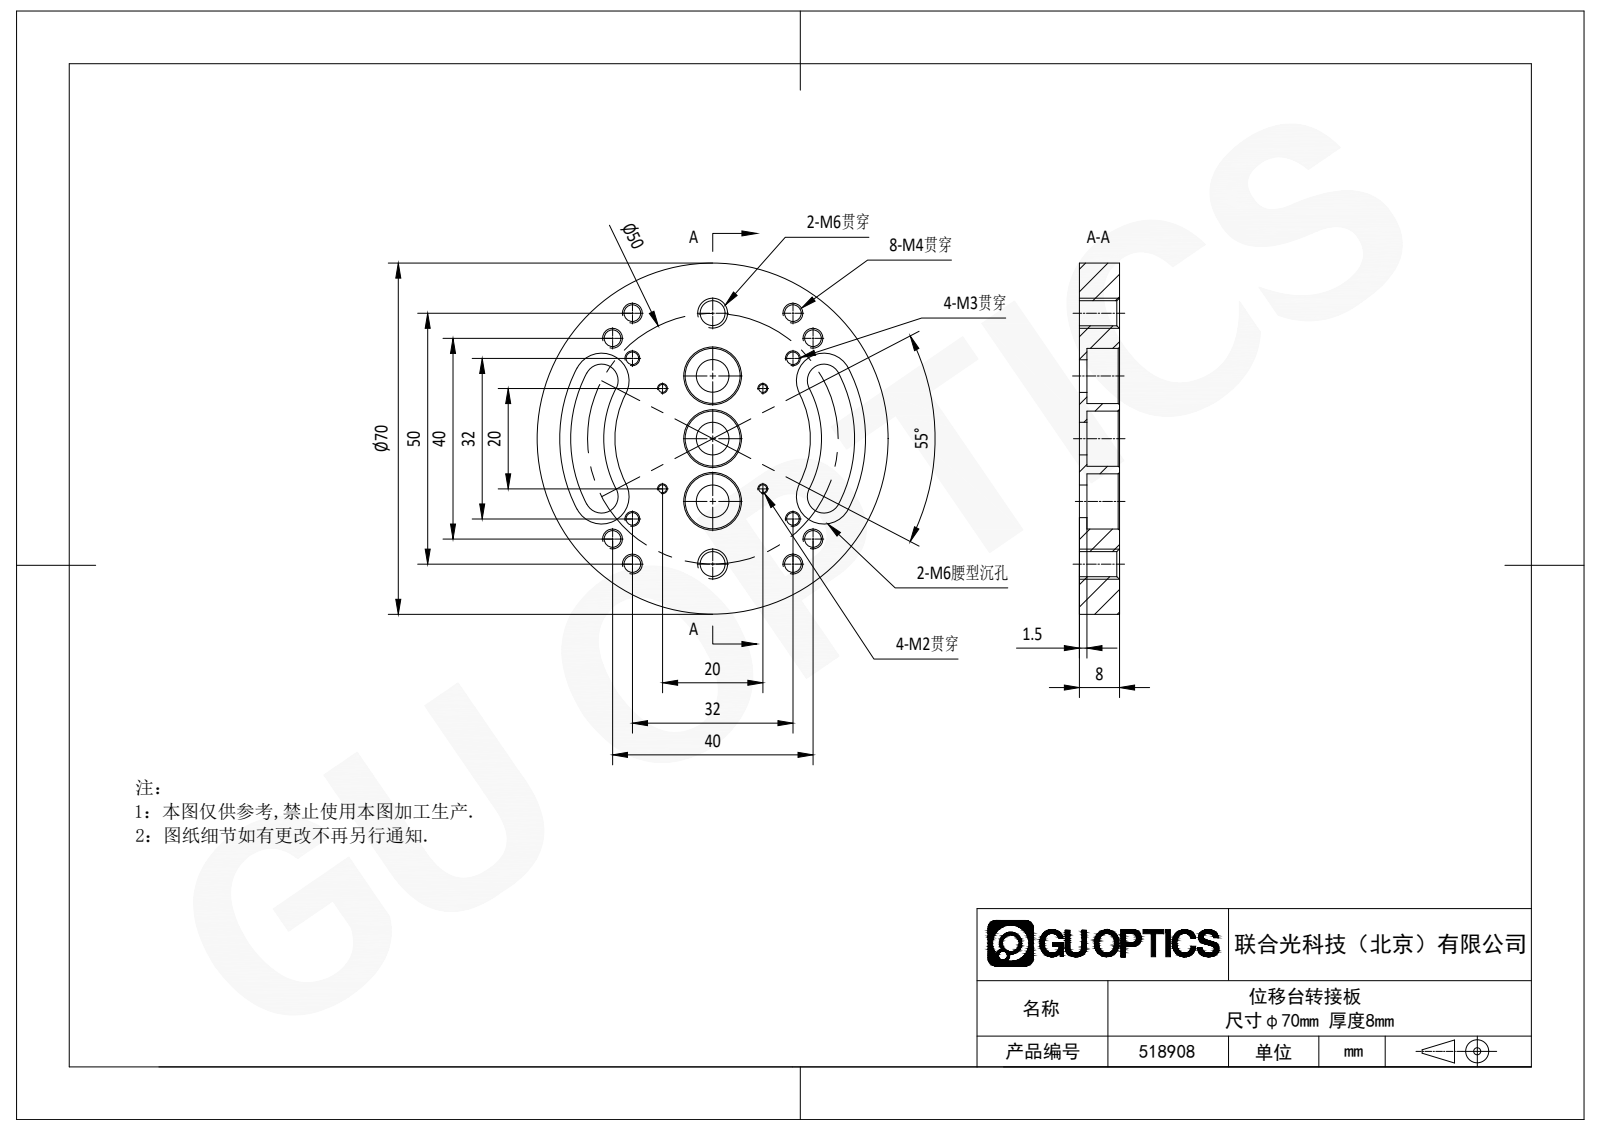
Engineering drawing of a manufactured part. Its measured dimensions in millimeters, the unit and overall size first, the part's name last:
Units: millimetres
Overall size (bounding box): 70 × 70 × 8
Round holes (diameter × count): ⌀3.3 ×8, ⌀1.6 ×4, ⌀2.5 ×4, ⌀6.5 ×3, ⌀11 ×3, ⌀5 ×2
Round bosses / shafts (diameter × count): ⌀70 ×1
Partial cylindrical surfaces — rounded edges, fillets, slot ends (radius × count): R3.3 ×4, R5.5 ×4, R19.5 ×1, R21.7 ×1, R28.3 ×1, R30.5 ×1
Main face-to-face distances: 8, 1.5, 6.5
Hole centre spacings: 14.14, 26.68, 31.62, 36.22, 28.28, 32, 5.66, 6.4
Volume: 22 441 mm³ · Surface area: 11 540 mm²
Bodies: 1 solid, 69 faces (7 planar, 41 cylindrical, 21 other)
STEP written by: SolidWorks 2020 (CONFIG_CONTROL_DESIGN)
